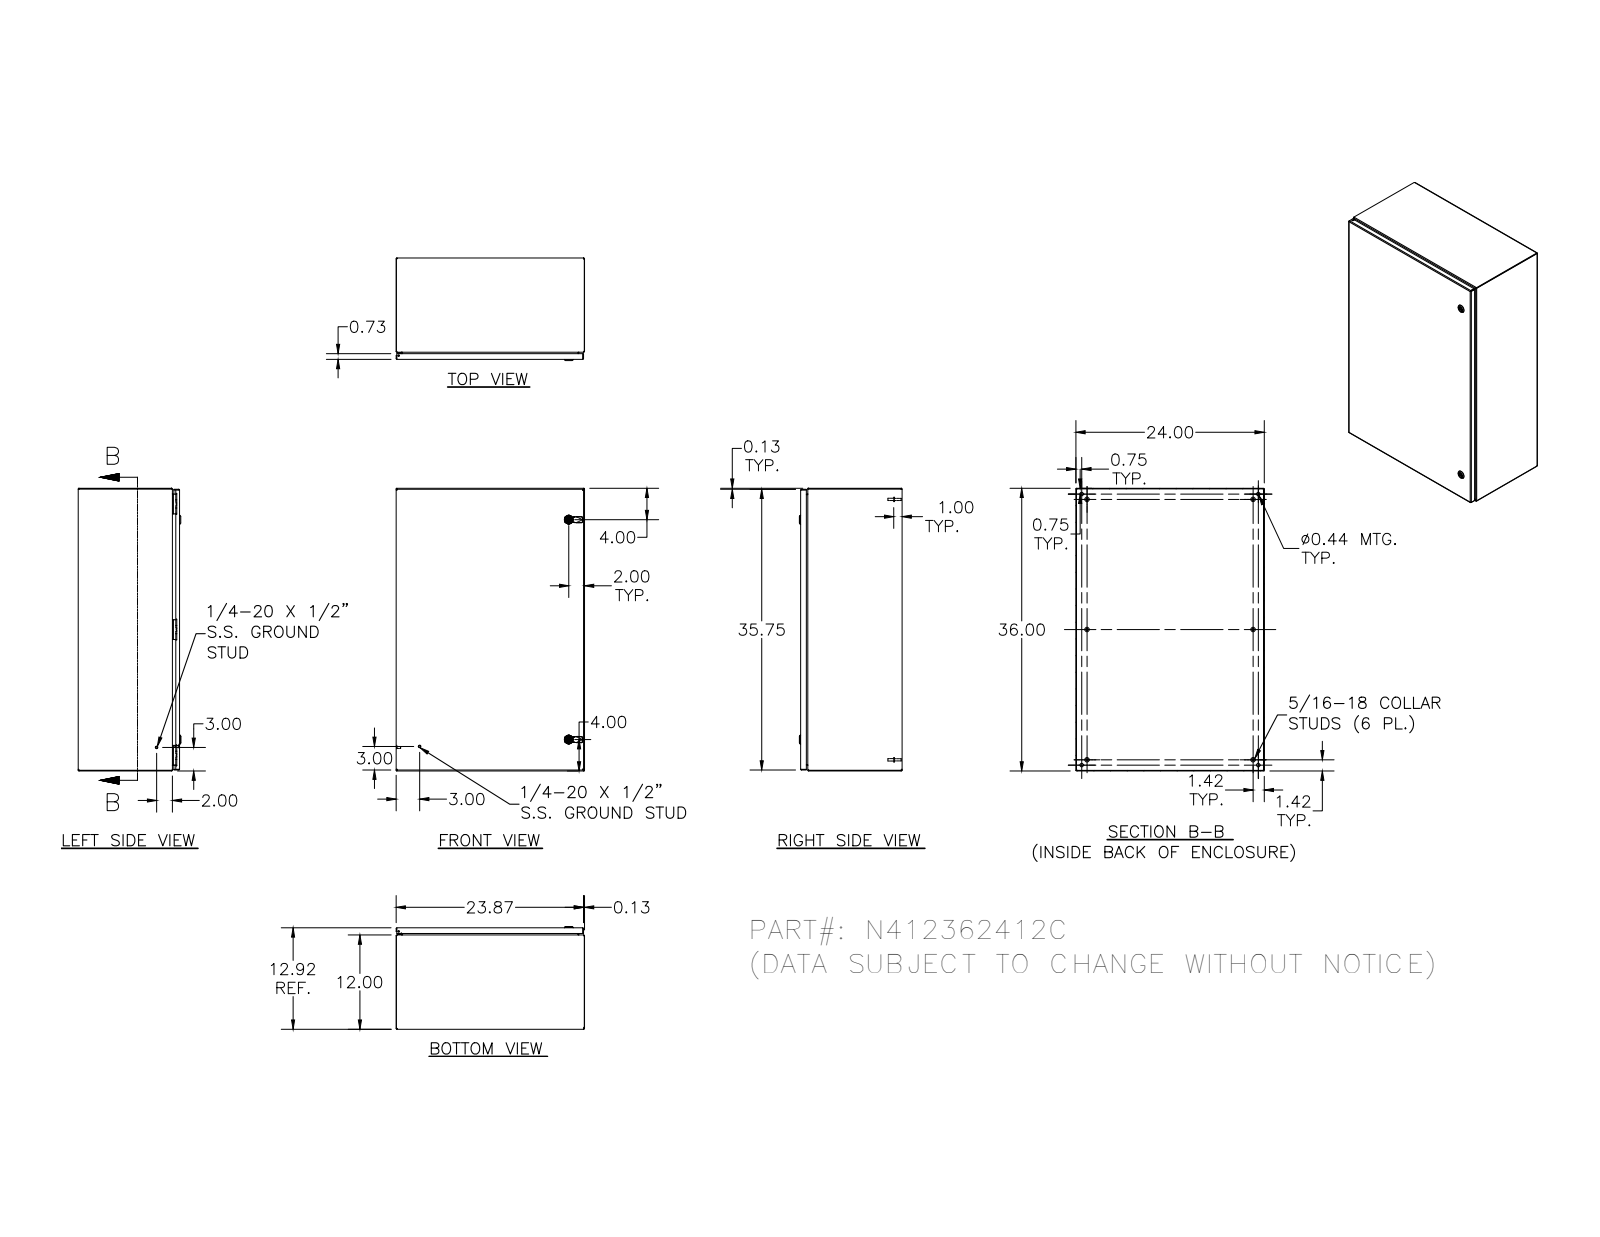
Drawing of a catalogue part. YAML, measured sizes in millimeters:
part_name: "N412362412C; N4123624CLID; 35124; 1000-u155_asm (+8 more)"
step_written_by: "Autodesk Inventor 2011 (AUTOMOTIVE_DESIGN)"
units: millimeters
bodies: {solids: 49, faces: 2252, planar: 831, cylindrical: 856, other: 565}
overall_size: [914.4, 609.6, 332.1]
volume: 4139000
surface_area: 4432000
round_holes:
  - {diameter: 4.8, count: 7}
  - {diameter: 2.4, count: 6}
  - {diameter: 3.9, count: 6}
  - {diameter: 4.2, count: 6}
  - {diameter: 4.4, count: 6}
  - {diameter: 11.1, count: 4}
  - {diameter: 4, count: 3}
  - {diameter: 5, count: 2}
  - {diameter: 8, count: 2}
  - {diameter: 10, count: 2}
  - {diameter: 10.2, count: 2}
  - {diameter: 16.1, count: 2}
round_bosses_or_shafts:
  - {diameter: 6.4, count: 14}
  - {diameter: 14.3, count: 6}
  - {diameter: 9.1, count: 6}
  - {diameter: 8.1, count: 6}
  - {diameter: 7.6, count: 6}
  - {diameter: 7, count: 6}
  - {diameter: 6.5, count: 6}
  - {diameter: 4.2, count: 6}
partial_cylinders:
  - {radius: 0.3, count: 54}
  - {radius: 1.3, count: 38}
  - {radius: 0.8, count: 34}
  - {radius: 0.4, count: 26}
  - {radius: 3.2, count: 24}
  - {radius: 0.5, count: 23}
  - {radius: 2.7, count: 20}
  - {radius: 0.8, count: 12}
face_to_face_distances: [1.9, 326.2, 1.9, 324.3, 328.1, 912.5, 607.7, 605.8, 607.7, 609.6]
hole_center_spacings: [406.4, 812.8, 16.8, 33.2, 406.6, 12.7, 16.7, 33.3]
